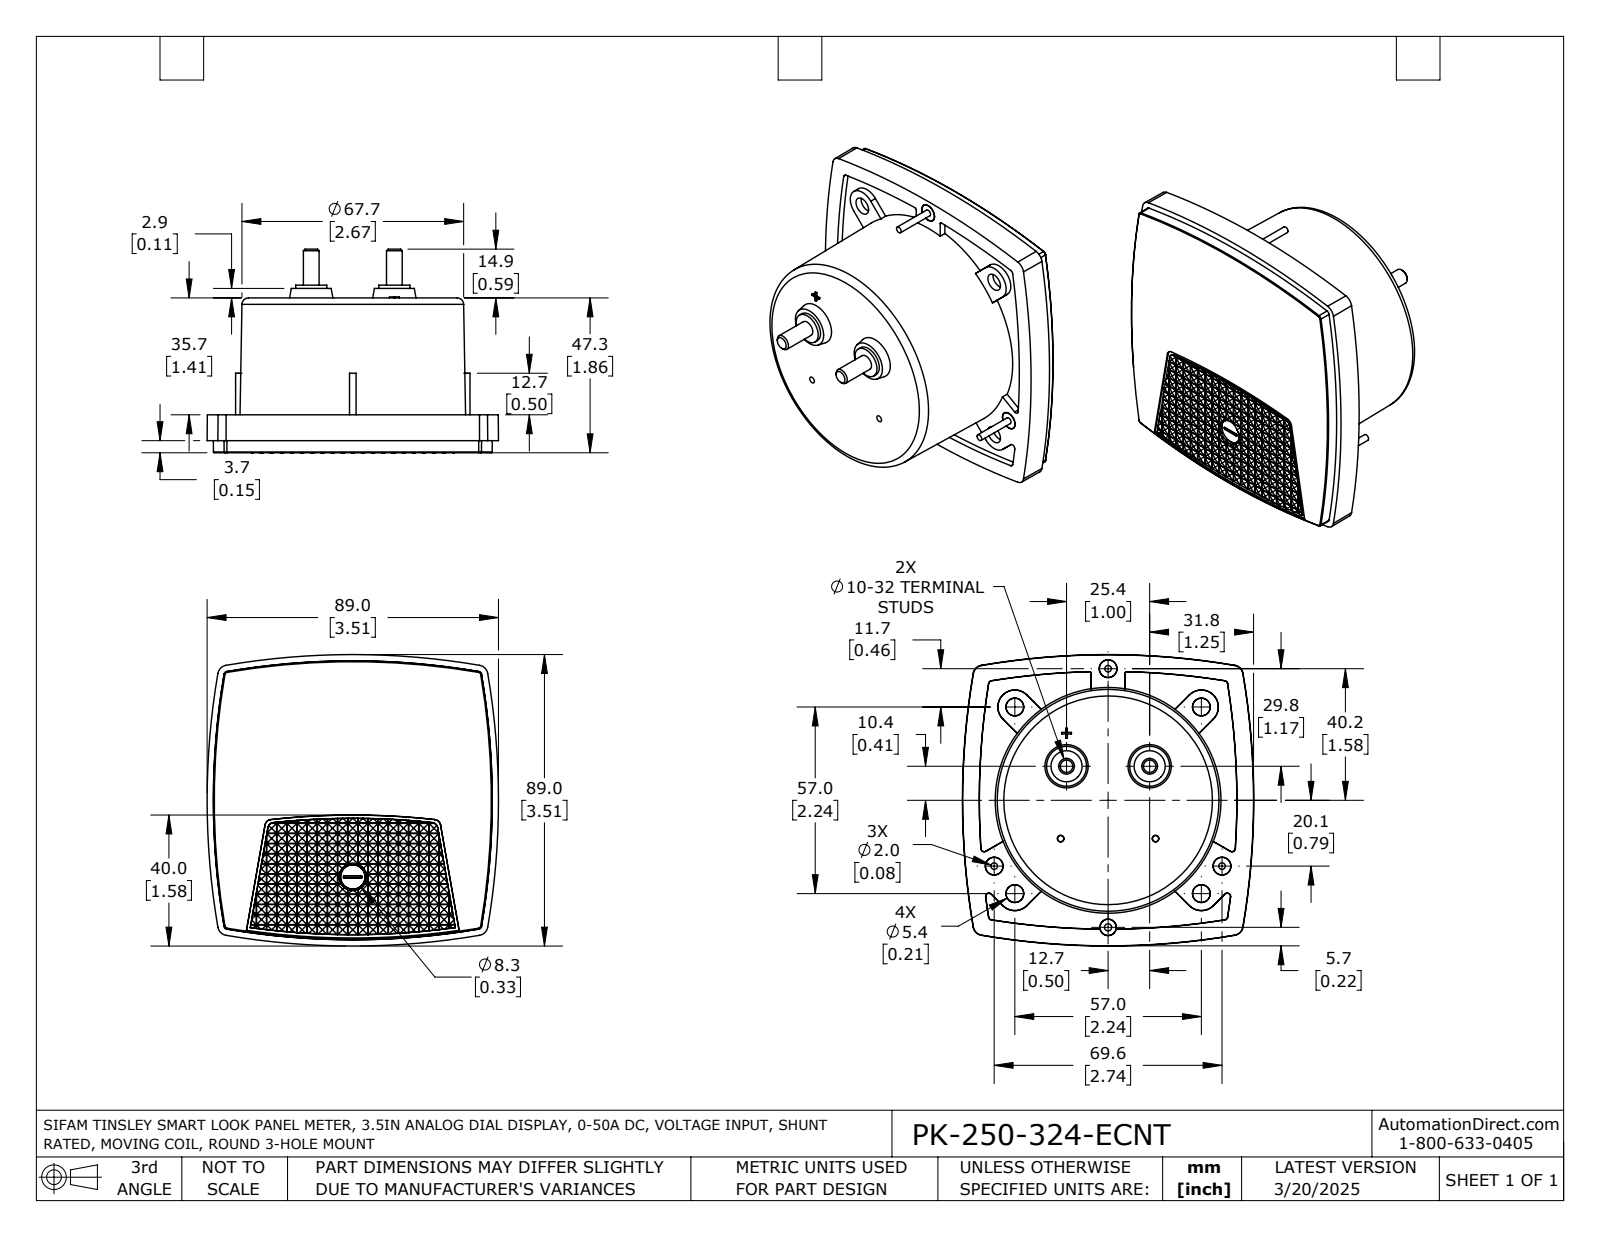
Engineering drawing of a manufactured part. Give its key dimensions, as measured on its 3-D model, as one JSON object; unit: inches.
{"part_name": "PK-250-324-ECNT", "step_written_by": "SolidWorks 2021 (AUTOMOTIVE_DESIGN)", "units": "inches", "bodies": {"solids": 1, "faces": 1078, "planar": 950, "cylindrical": 23, "other": 105}, "overall_size": [3.505, 3.505, 2.453], "volume_in3": 12.99, "surface_area_in2": 44.29, "round_holes": [[0.087, 1]], "round_bosses_or_shafts": [[0.213, 3], [0.079, 3], [0.374, 2], [0.189, 2]], "partial_cylinders_radius": [[8.961, 1]], "face_to_face_distances": [1.862, 1.406, 0.457, 0.079, 1.484, 0.378, 0.024, 0.096, 0.072, 0.12]}
